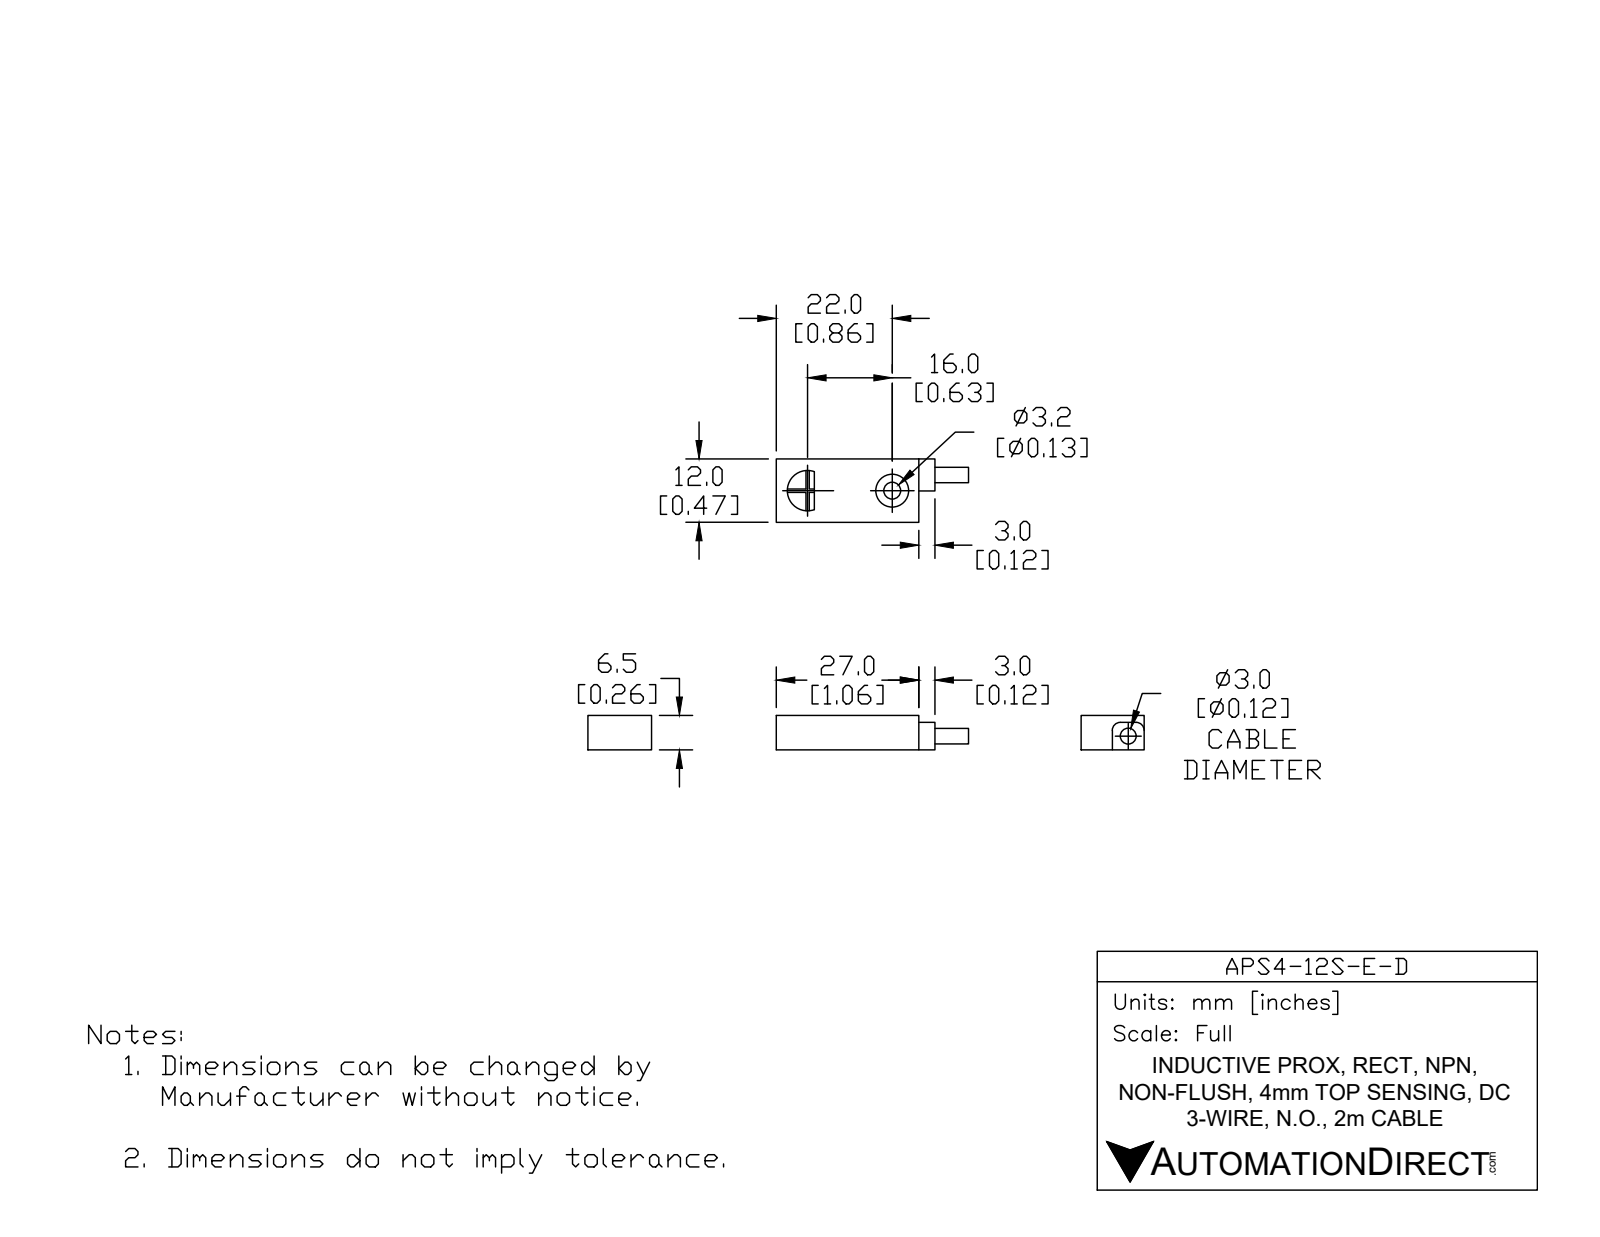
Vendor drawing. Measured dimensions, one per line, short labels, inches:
name: APS4-12S-E_bracket_1; APS4-12S-E_BODY_1; APS4-12S-E-D
written by: SolidWorks 2017 (AUTOMOTIVE_DESIGN)
unit: in
bodies: 4 solids, 88 faces (60 planar, 28 cylindrical, 0 other)
size: 1.611 × 0.516 × 0.281
volume: 0.08 in³; area: 5.175 in²
holes: 1× ⌀0.081, 1× ⌀0.126, 1× ⌀0.217, 1× ⌀0.232, 1× ⌀0.245
bosses: 1× ⌀0.345, 1× ⌀0.226, 1× ⌀0.112
rounds: 8× R0.005, 4× R0.02, 2× R0.031
face distances: 0.05, 0.256, 0.268, 0.422, 0.28, 0.022, 0.258, 0.246, 0.472, 0.218
hole spacings: 0.629
